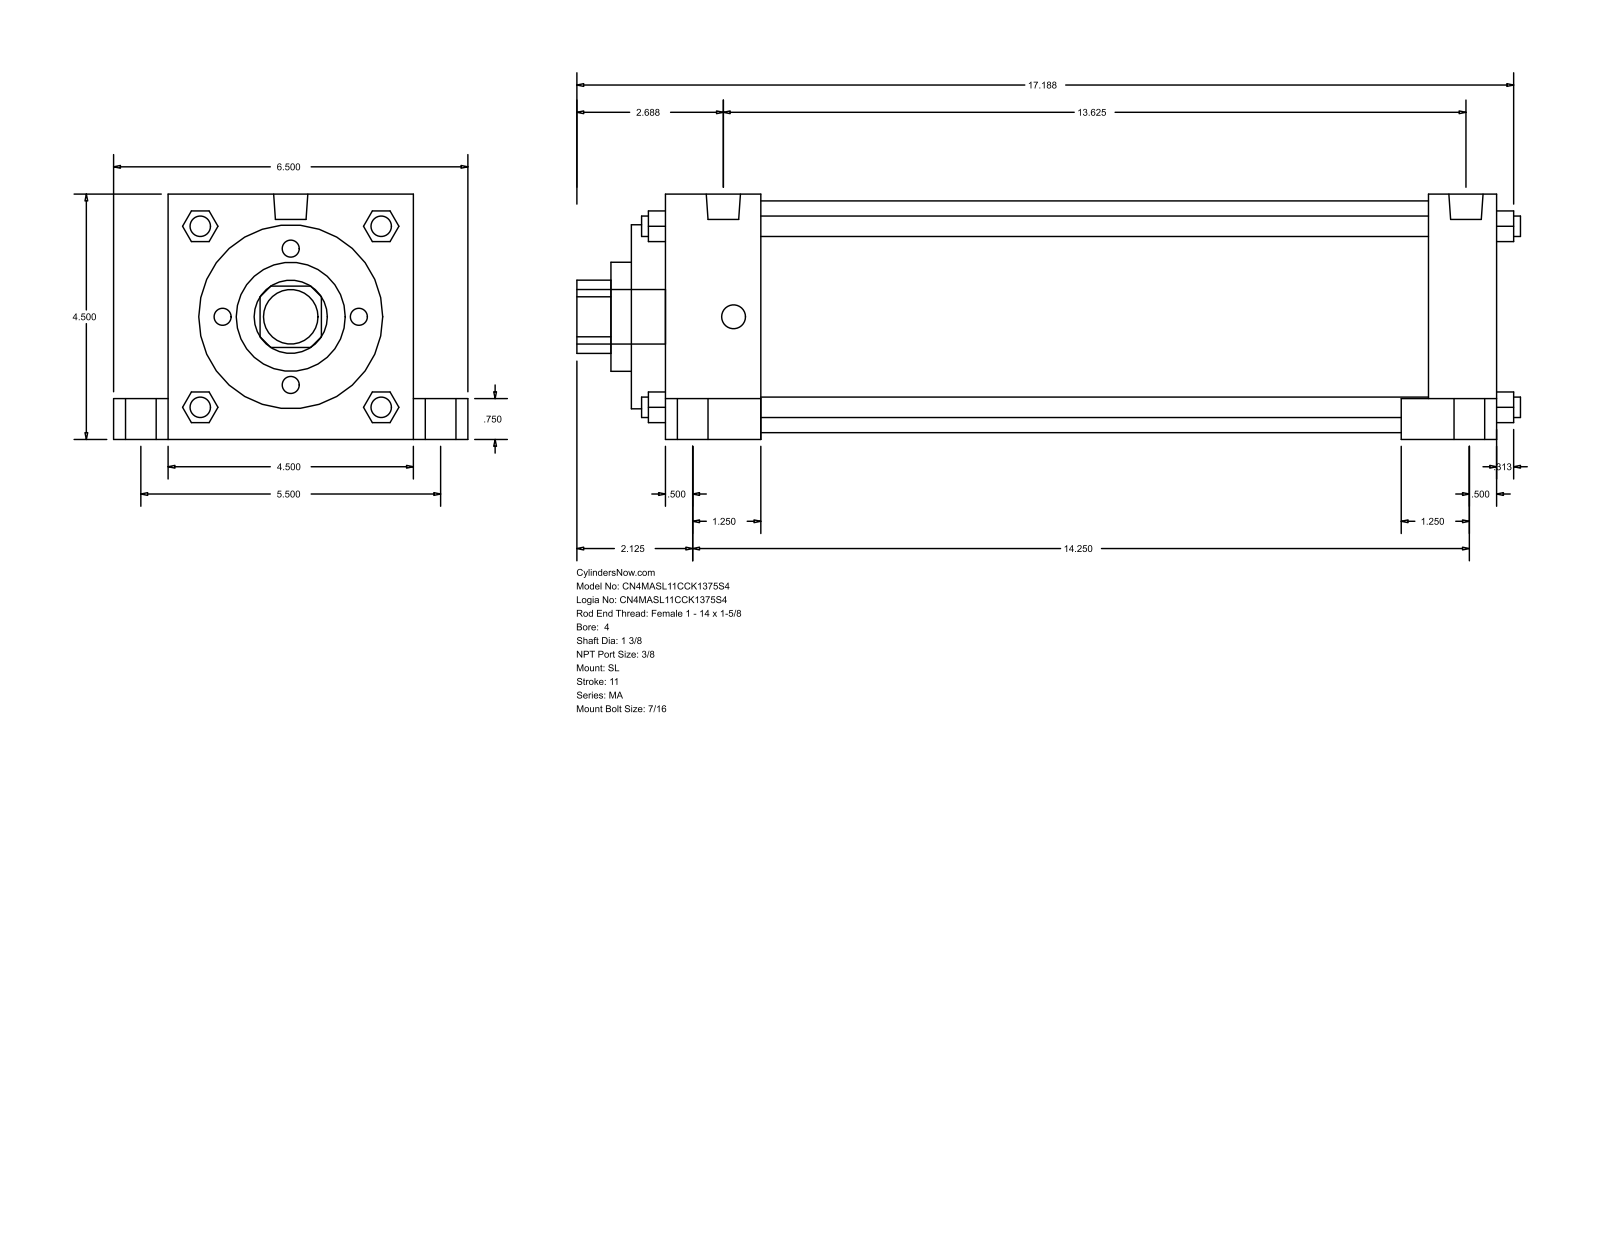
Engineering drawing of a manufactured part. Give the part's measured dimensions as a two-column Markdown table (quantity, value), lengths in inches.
| quantity | value |
| --- | --- |
| part name | MA_SL__0400_1.375 |
| STEP written by | GSSL Pune (CONFIG_CONTROL_DESIGN) |
| units | inches |
| bodies | 0 solids, 150 faces (113 planar, 37 cylindrical, 0 other) |
| overall size | 17.313 × 6.5 × 4.5 |
| round holes (diameter × count) | 1.375 × 1, 2 × 1, 3.375 × 1, 4.25 × 1 |
| round bosses / shafts (diameter × count) | 0.813 × 4, 0.563 × 4, 0.437 × 4, 0.375 × 4, 0.627 × 2, 1 × 1 |
| partial cylindrical surfaces (radius × count) | 0.672 × 1 |
| main face-to-face distances | 4.5, 15.25, 15.875, 0.625, 2.375, 1.75, 13.5, 14.625, 14, 12.25 |
